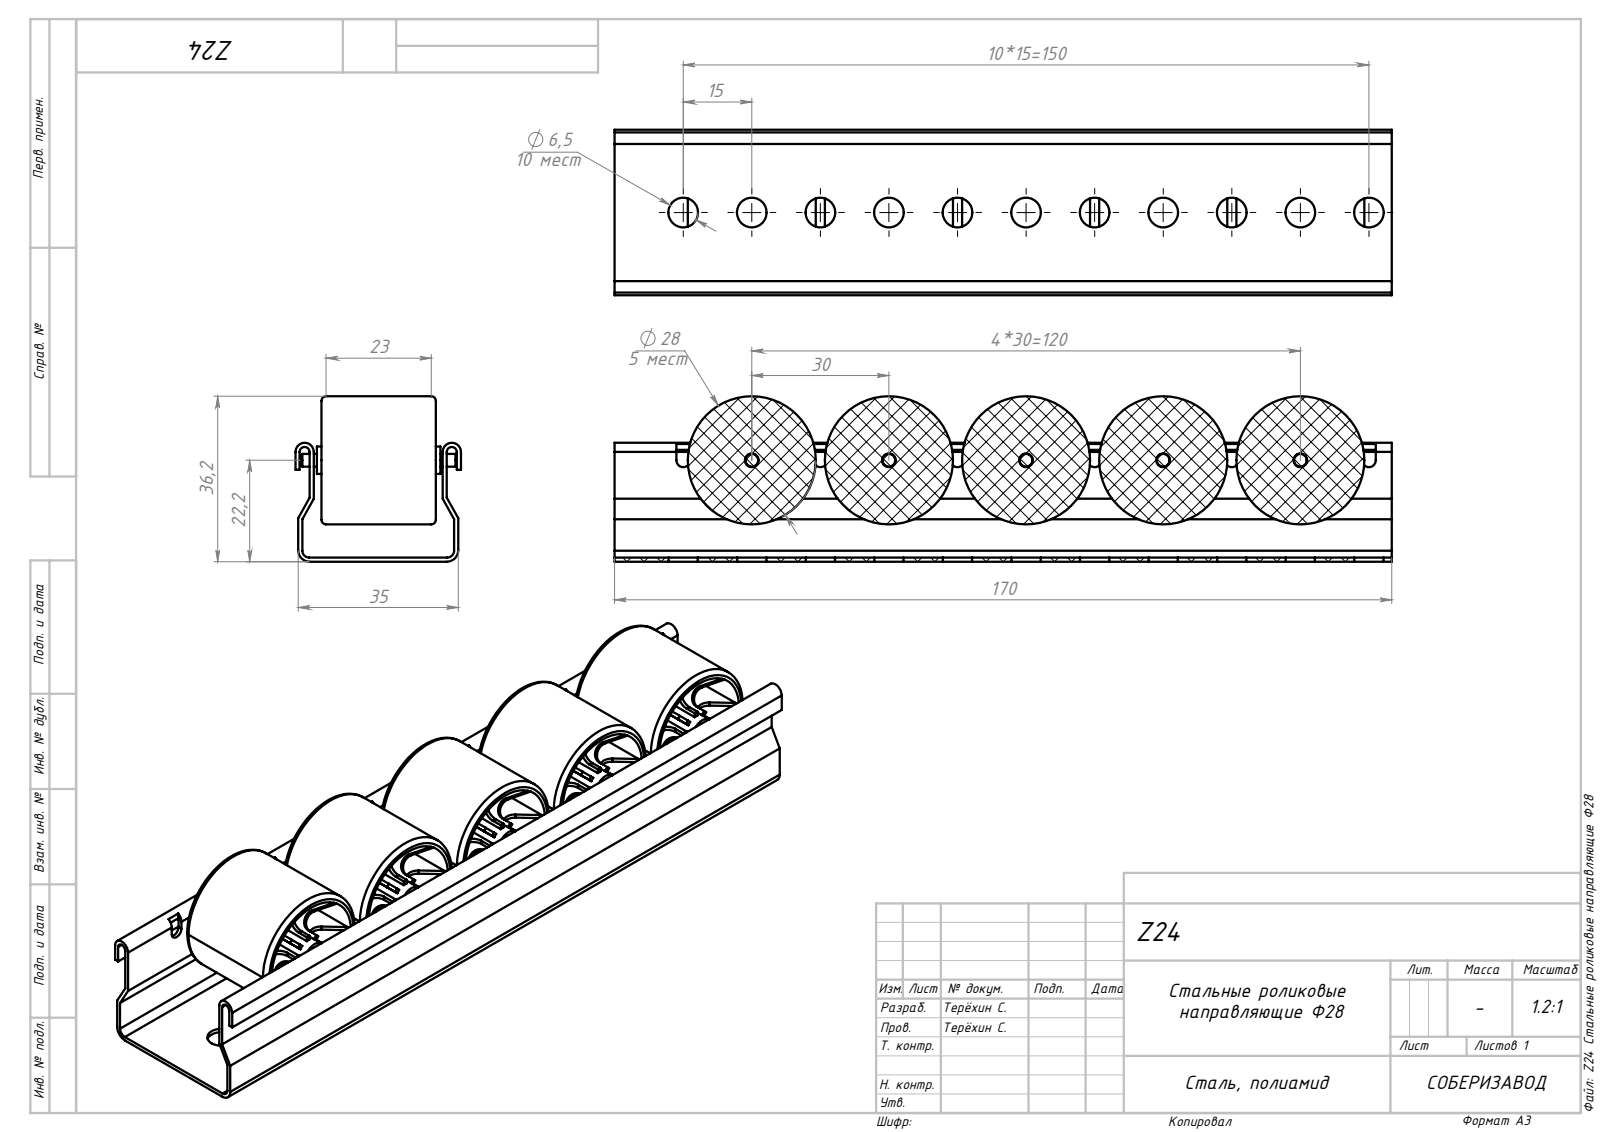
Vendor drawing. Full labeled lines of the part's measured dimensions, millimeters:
Part name (STEP PRODUCT): Z24 Стальные роликовые направляющие Ф28
STEP written by: SolidWorks 2022 (AUTOMOTIVE_DESIGN)
Units: millimetres
Bodies: 11 solids, 818 faces (565 planar, 213 cylindrical, 40 other)
Overall size (bounding box): 170 × 36.2 × 36.17
Volume: 43 865 mm³ · Surface area: 74 900 mm²
Round holes (diameter × count): ⌀3 ×11, ⌀6.5 ×11, ⌀24.5 ×5
Round bosses / shafts (diameter × count): ⌀28 ×5, ⌀6 ×5, ⌀2.8 ×5
Partial cylindrical surfaces — rounded edges, fillets, slot ends (radius × count): R2.5 ×66, R1.1 ×2, R1.5 ×2, R2 ×2
Main face-to-face distances: 0.9, 2.5, 21.21, 31.6, 42.42, 0.85, 29.1, 30, 0.6, 3.1
Hole centre spacings: 15, 30, 45, 60, 75, 90, 105, 120
